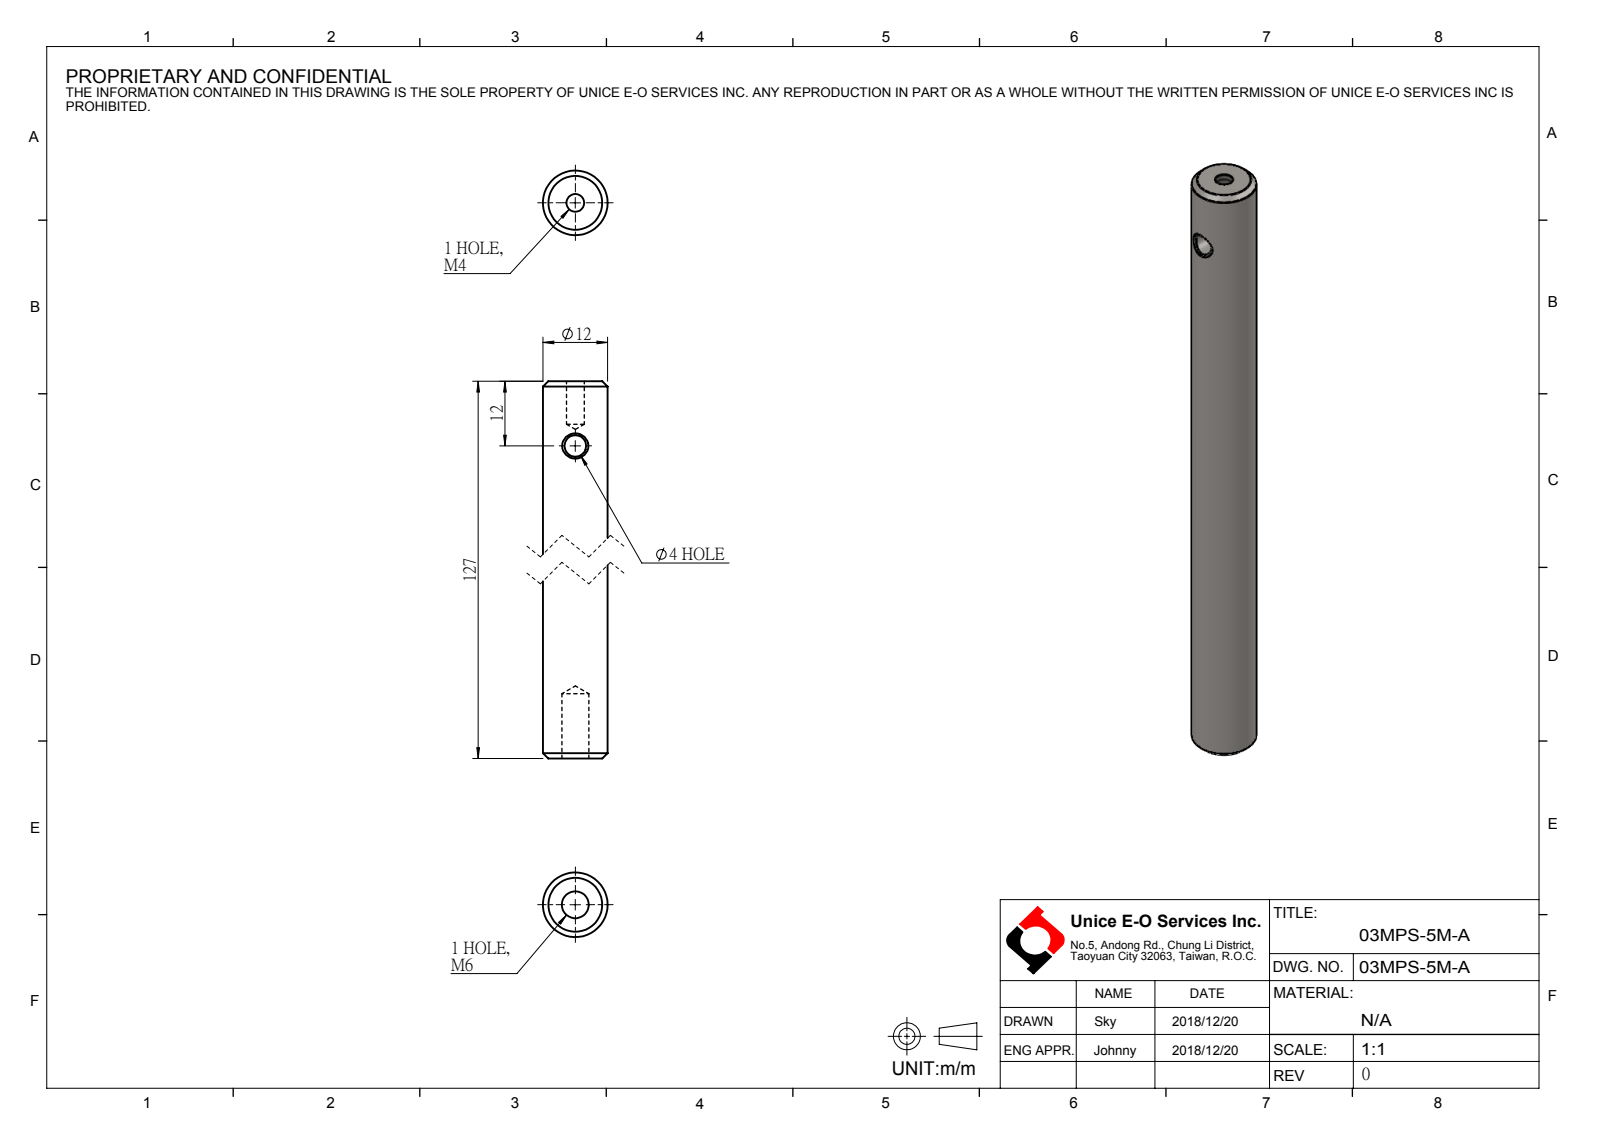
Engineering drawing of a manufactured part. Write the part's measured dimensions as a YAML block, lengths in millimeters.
part_name: "03MPS-5M-A"
step_written_by: "SolidWorks 2016 (AUTOMOTIVE_DESIGN)"
units: millimeters
bodies: {solids: 0, faces: 18, planar: 2, cylindrical: 8, other: 8}
overall_size: [127, 12, 12]
round_holes:
  - {diameter: 3.3, count: 1}
  - {diameter: 4, count: 1}
  - {diameter: 5, count: 1}
round_bosses_or_shafts:
  - {diameter: 12, count: 1}
face_to_face_distances: [127]
